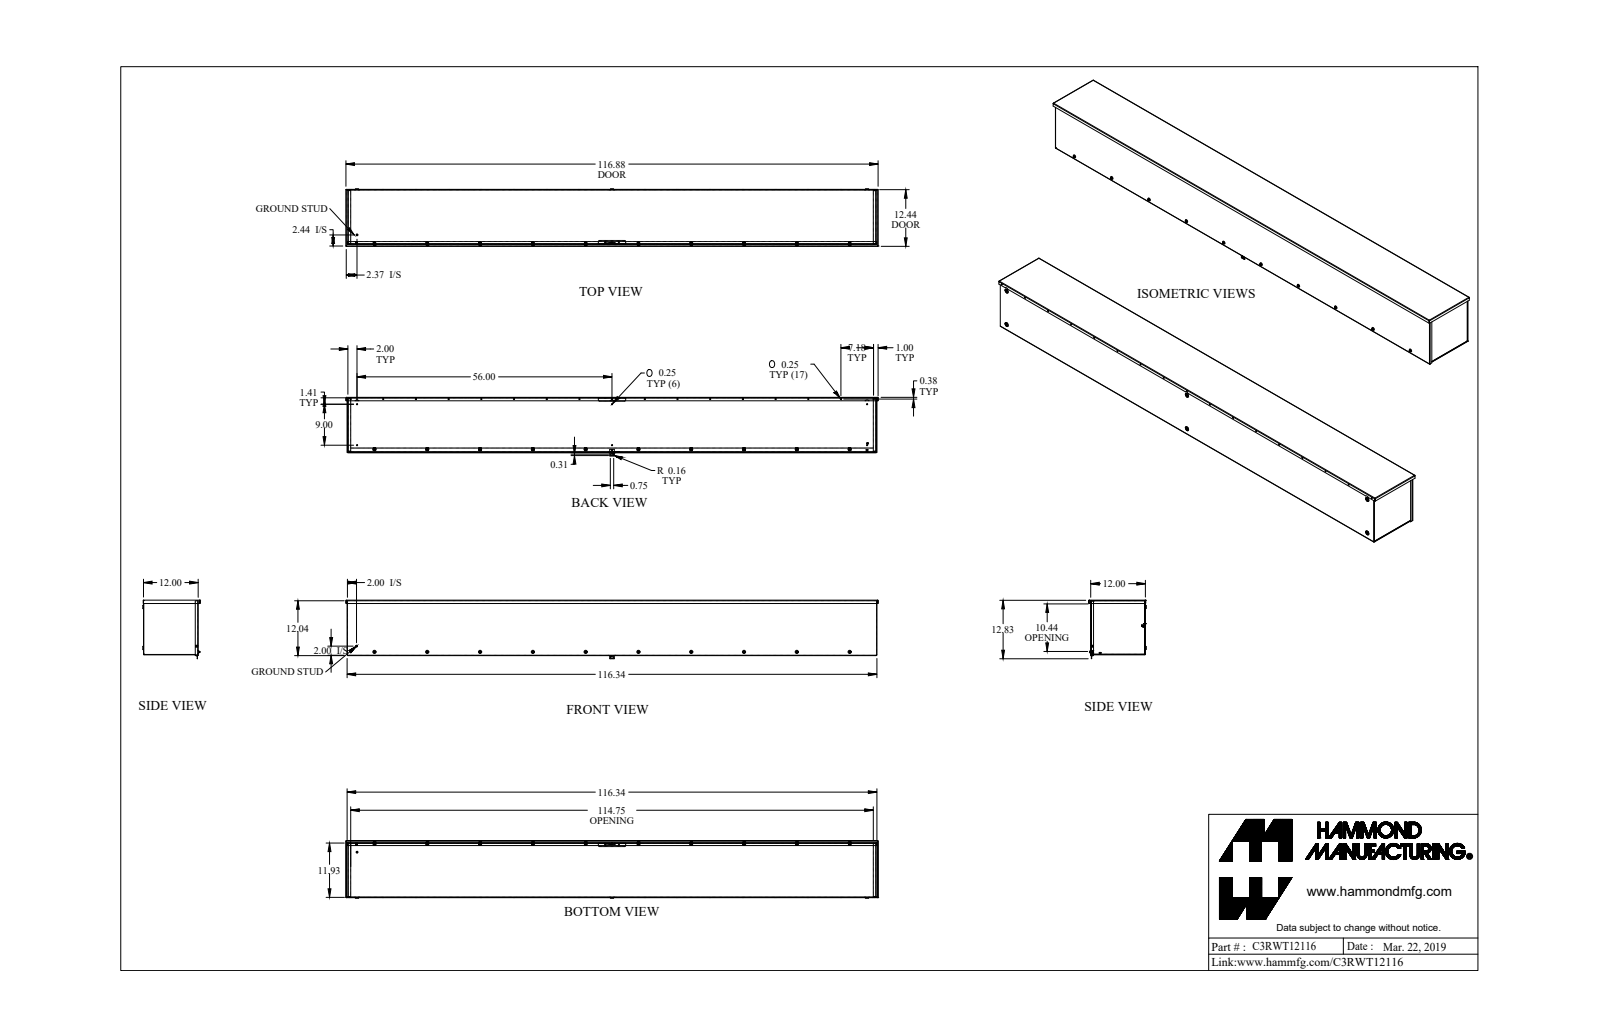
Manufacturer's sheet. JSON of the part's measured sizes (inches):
{"part_name": "C3RWT12116_Default", "step_written_by": "SolidWorks 2019 (CONFIG_CONTROL_DESIGN)", "units": "inches", "bodies": {"solids": 44, "faces": 1696, "planar": 925, "cylindrical": 547, "other": 224}, "overall_size": [116.875, 12.871, 12.594], "volume_in3": 453.3, "surface_area_in2": 12679, "round_holes": [[0.25, 25], [0.156, 12], [0.214, 10], [0.23, 10], [0.203, 2], [0.125, 1], [0.137, 1], [0.2, 1], [0.215, 1]], "round_bosses_or_shafts": [[0.19, 11], [0.148, 10], [0.375, 2], [0.5, 1], [0.367, 1], [0.21, 1], [0.152, 1], [0.125, 1]], "partial_cylinders_radius": [[0.08, 40], [0.108, 40], [0.022, 20], [0.036, 18], [0.108, 18], [0.125, 18], [0.171, 10], [0.206, 10]], "face_to_face_distances": [0.072, 11.928, 12, 0.072, 11.856, 11.856, 11.928, 115.928, 0.144, 12.366], "hole_center_spacings": [11.594, 14.359, 21.539, 7.18, 35.898, 7.18, 23.187, 23.188]}
